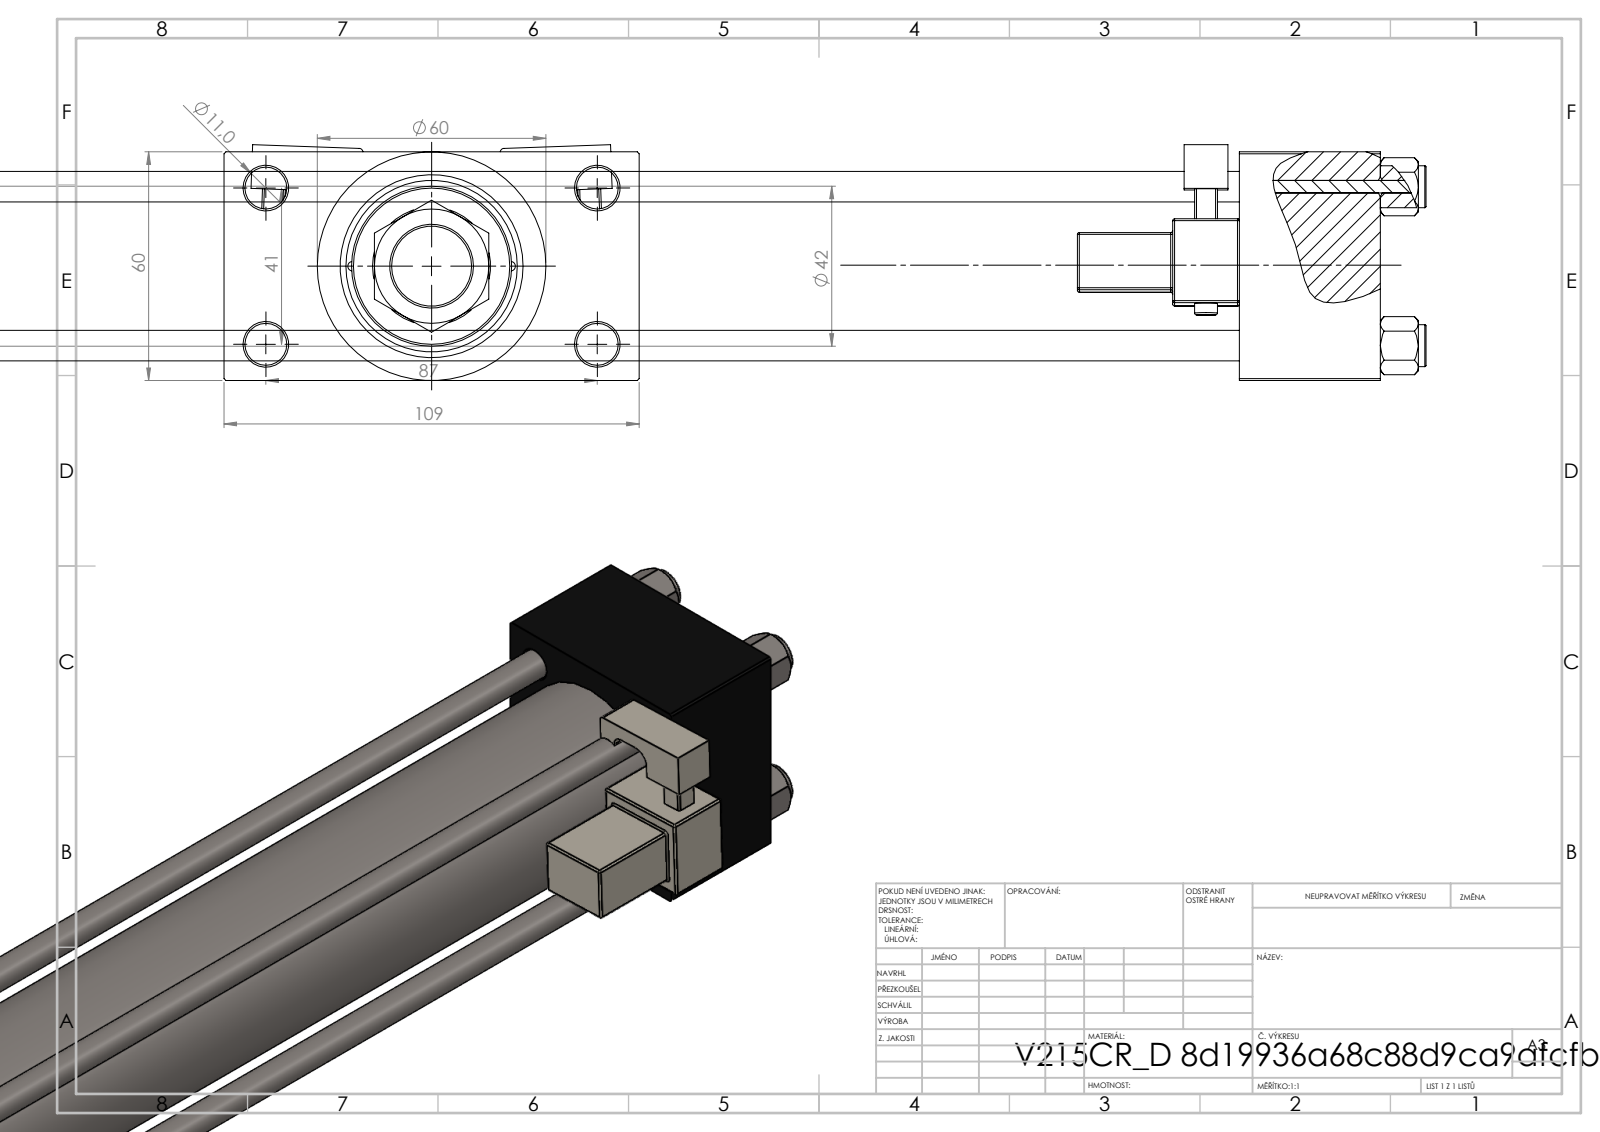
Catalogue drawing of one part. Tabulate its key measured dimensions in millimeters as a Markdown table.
| quantity | value |
| --- | --- |
| part name | MFA; V215CR_D_TYCINKA; V215CR_D_Body; V215_VC_A (+3 more) |
| STEP written by | SolidWorks 2019 (CONFIG_CONTROL_DESIGN) |
| units | millimeters |
| bodies | 14 solids, 1320 faces (576 planar, 156 cylindrical, 588 other) |
| overall size | 610 × 109 × 61.9 |
| volume | 1 059 000 mm³ |
| surface area | 321 048 mm² |
| round holes (diameter × count) | 8 × 4, 11 × 4, 2.5 × 2, 7 × 2, 16.66 × 2, 24 × 2, 18.5 × 1, 28 × 1, 31 × 1, 40 × 1, 45 × 1 |
| round bosses / shafts (diameter × count) | 11 × 4, 6 × 2, 60 × 1, 46 × 1, 42 × 1, 22 × 1, 14 × 1 |
| partial cylindrical surfaces (radius × count) | 0.5 × 48, 1 × 2, 2.5 × 2, 4 × 2, 13.5 × 1 |
| main face-to-face distances | 60, 438, 24.5, 84.5, 37, 475, 518, 481, 43, 109 |
| hole center spacings | 20.85, 22.65, 29.49, 30.62, 41.7, 46.53, 47.15, 48.09 |
